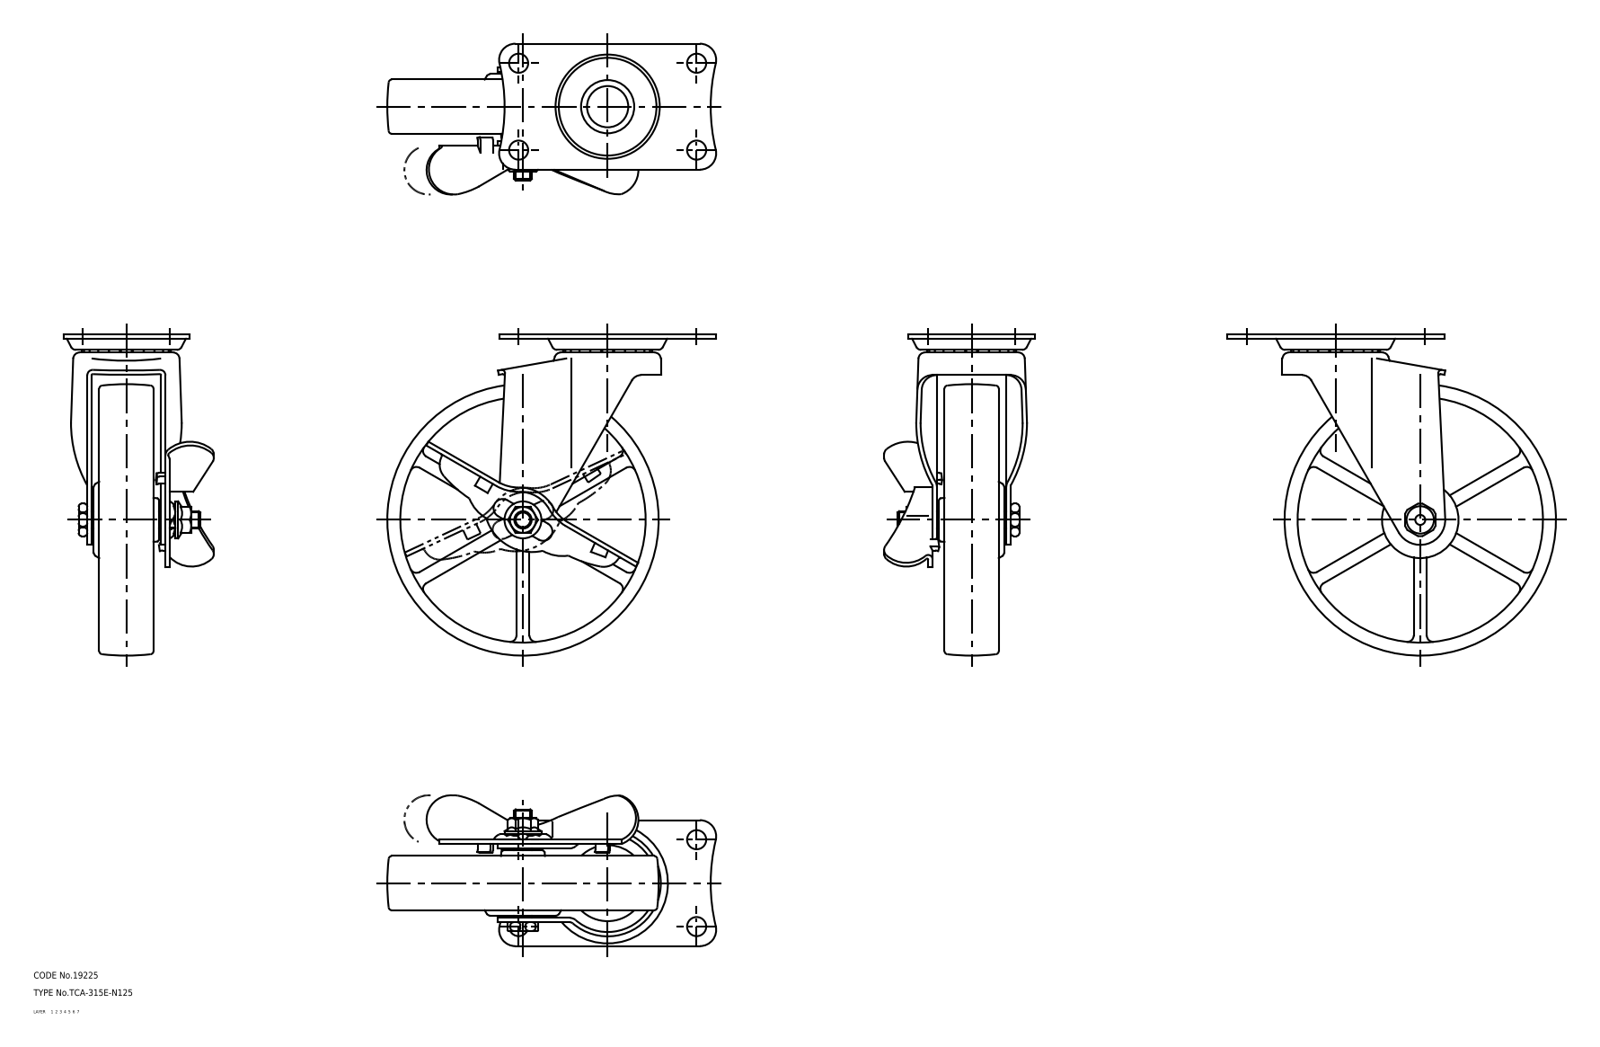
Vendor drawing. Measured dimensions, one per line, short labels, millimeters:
name: 67154040; 67154053; 67154066; 67154079 (+2 more)
written by: CADfix (AUTOMOTIVE_DESIGN)
unit: mm
bodies: 6 solids, 713 faces (0 planar, 0 cylindrical, 713 other)
size: 151.5 × 148 × 69.45
volume: 268 978 mm³; area: 89 304 mm²
